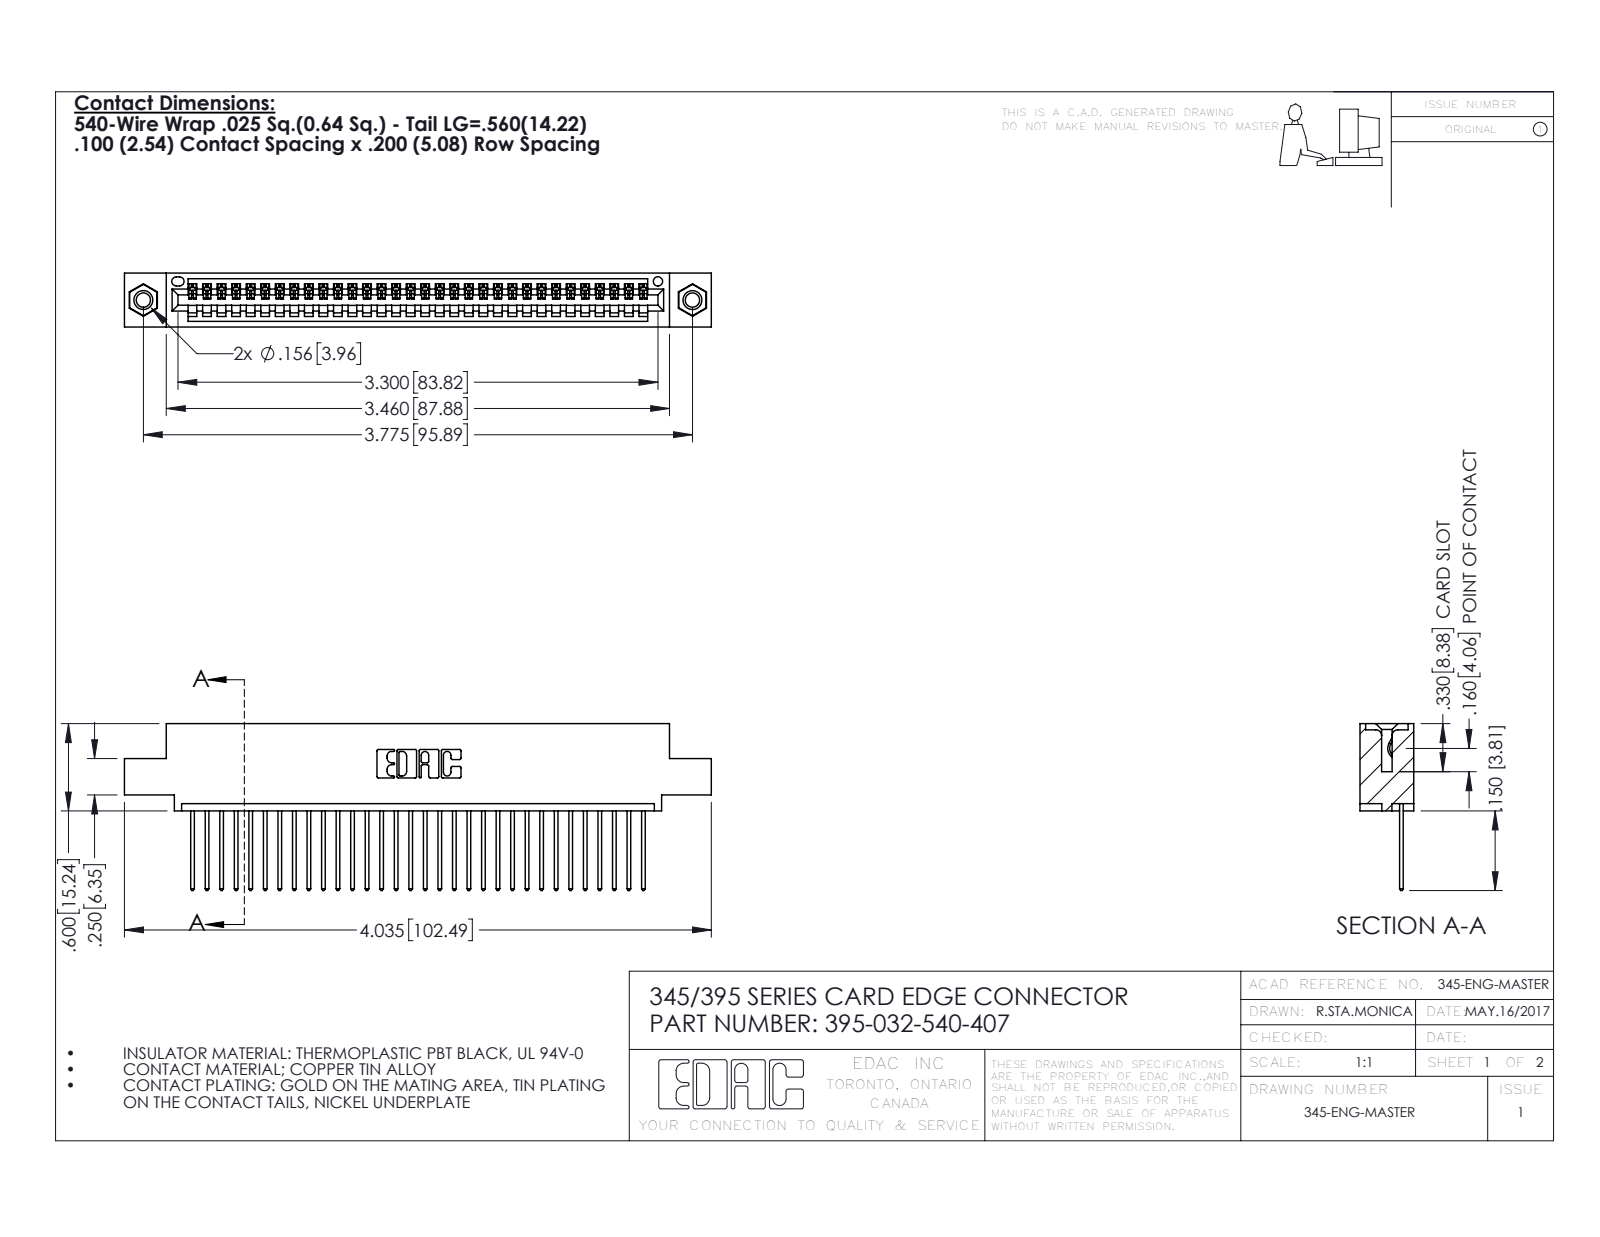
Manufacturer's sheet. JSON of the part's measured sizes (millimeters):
{"part_name": "395-032-540-407; 345-292-001_345-293-140; 345 Part_0.110 Offset - 0.156 Dia-TI; 345-250-001_345-250-005-103", "step_written_by": "SolidWorks 2016 (CONFIG_CONTROL_DESIGN)", "units": "millimeters", "bodies": {"solids": 35, "faces": 2046, "planar": 1396, "cylindrical": 634, "other": 16}, "overall_size": [102.5, 29.1, 9.4], "volume_mm3": 9600, "surface_area_mm2": 13060, "round_holes": [[2.5, 2], [3.2, 2], [4, 2], [1.6, 1]], "round_bosses_or_shafts": [[3.9, 2]], "partial_cylinders_radius": [[0.2, 64], [0.3, 64], [0.3, 22], [0.2, 6], [0.8, 6], [0.7, 3], [0.8, 2], [1, 2]], "face_to_face_distances": [1.8, 7.6, 9.4, 5.1, 2.5, 6.9, 0.6, 5.7, 3.8, 1.8], "hole_center_spacings": [6.9, 89.9, 95.9]}
